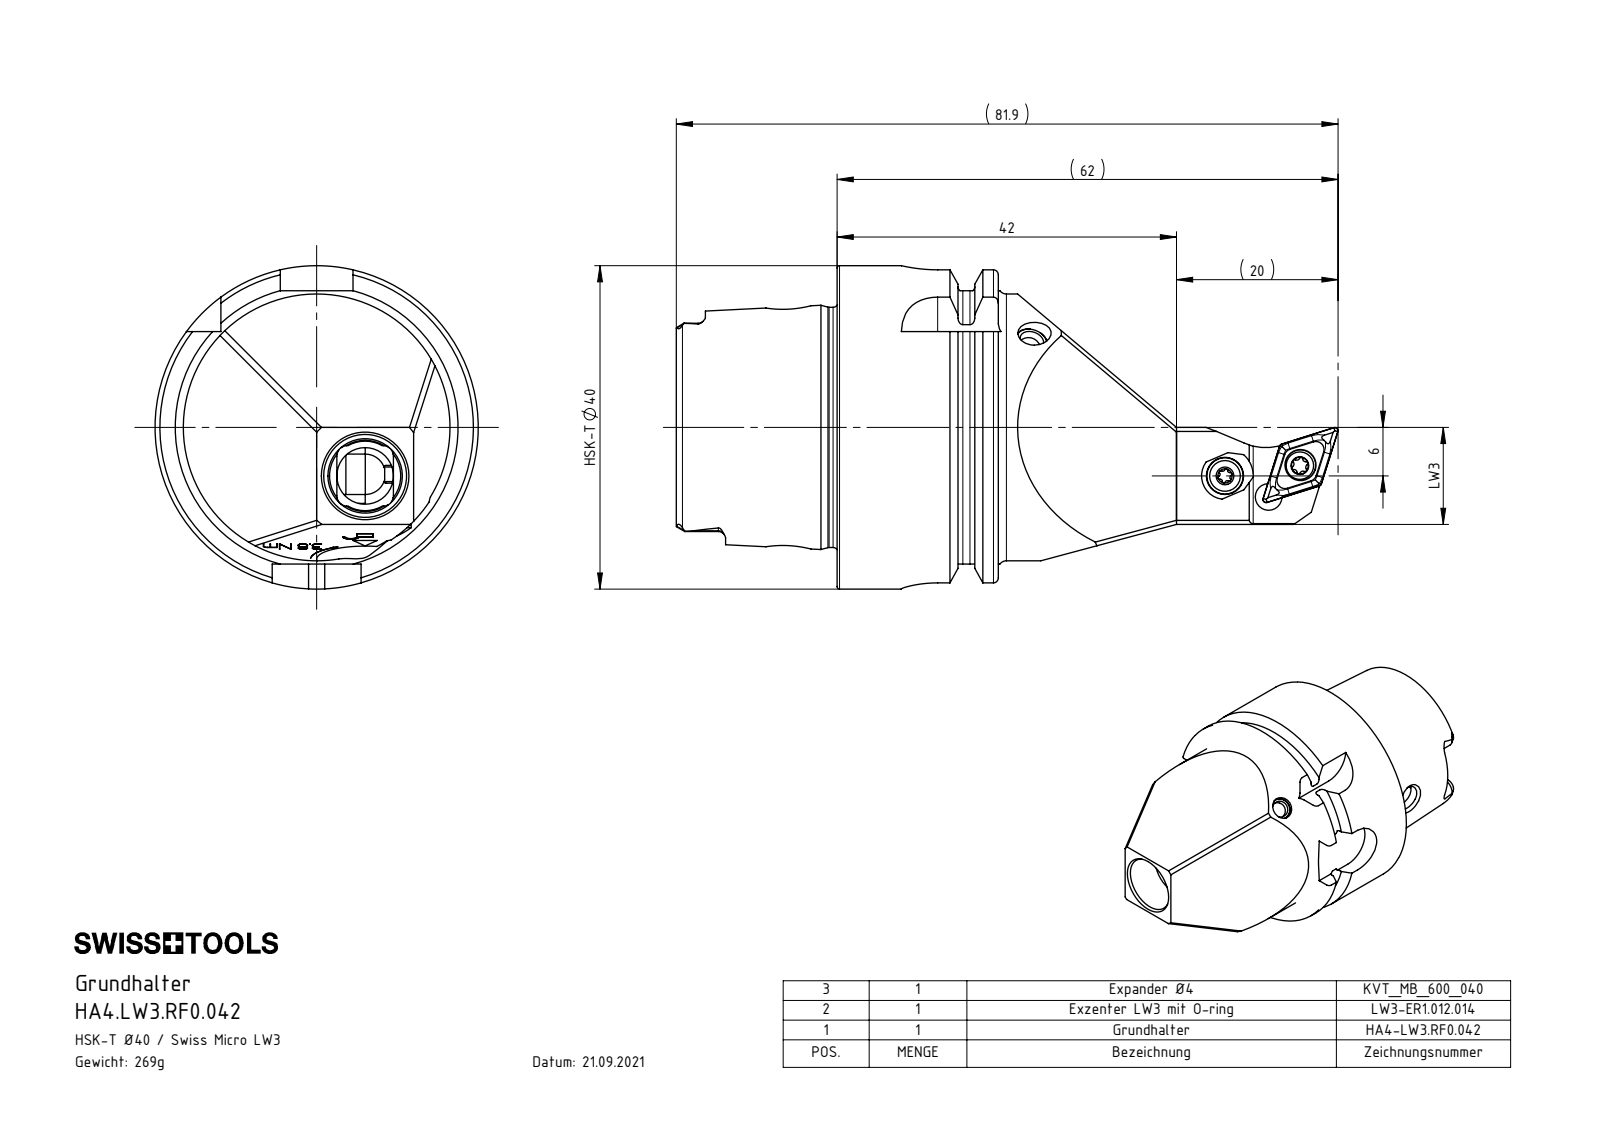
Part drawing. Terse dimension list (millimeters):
name: LW3-ER1.012.014_B_Standard<Wie bearbeitet>; KVT_MB_600_040; LW3-ER1.012.014; DIN 3771 - 7x1 (+2 more)
written by: SolidWorks 2017 (AUTOMOTIVE_DESIGN)
unit: mm
bodies: 6 solids, 270 faces (105 planar, 83 cylindrical, 82 other)
size: 61.9 × 40 × 40
volume: 34 359 mm³; area: 13 060 mm²
holes: 2× ⌀3.3, 1× ⌀1, 1× ⌀2.4, 1× ⌀3, 1× ⌀4.6, 1× ⌀5, 1× ⌀7, 1× ⌀9.21, 1× ⌀10, 1× ⌀11, 1× ⌀12, 1× ⌀12.5
bosses: 1× ⌀40, 1× ⌀34.75, 1× ⌀33, 1× ⌀29.71, 1× ⌀11.4, 1× ⌀9.5, 1× ⌀7.7, 1× ⌀4
rounds: 6× R0.34, 6× R0.59, 6× R0.9, 4× R1.3, 4× R1.88, 4× R4.5, 2× R2.5, 2× R3.7
face distances: 12, 7.95, 19.95, 19.9, 27.85, 39.85, 16.9, 35.7, 15.8, 7.85
hole spacings: 8.49, 32.56
